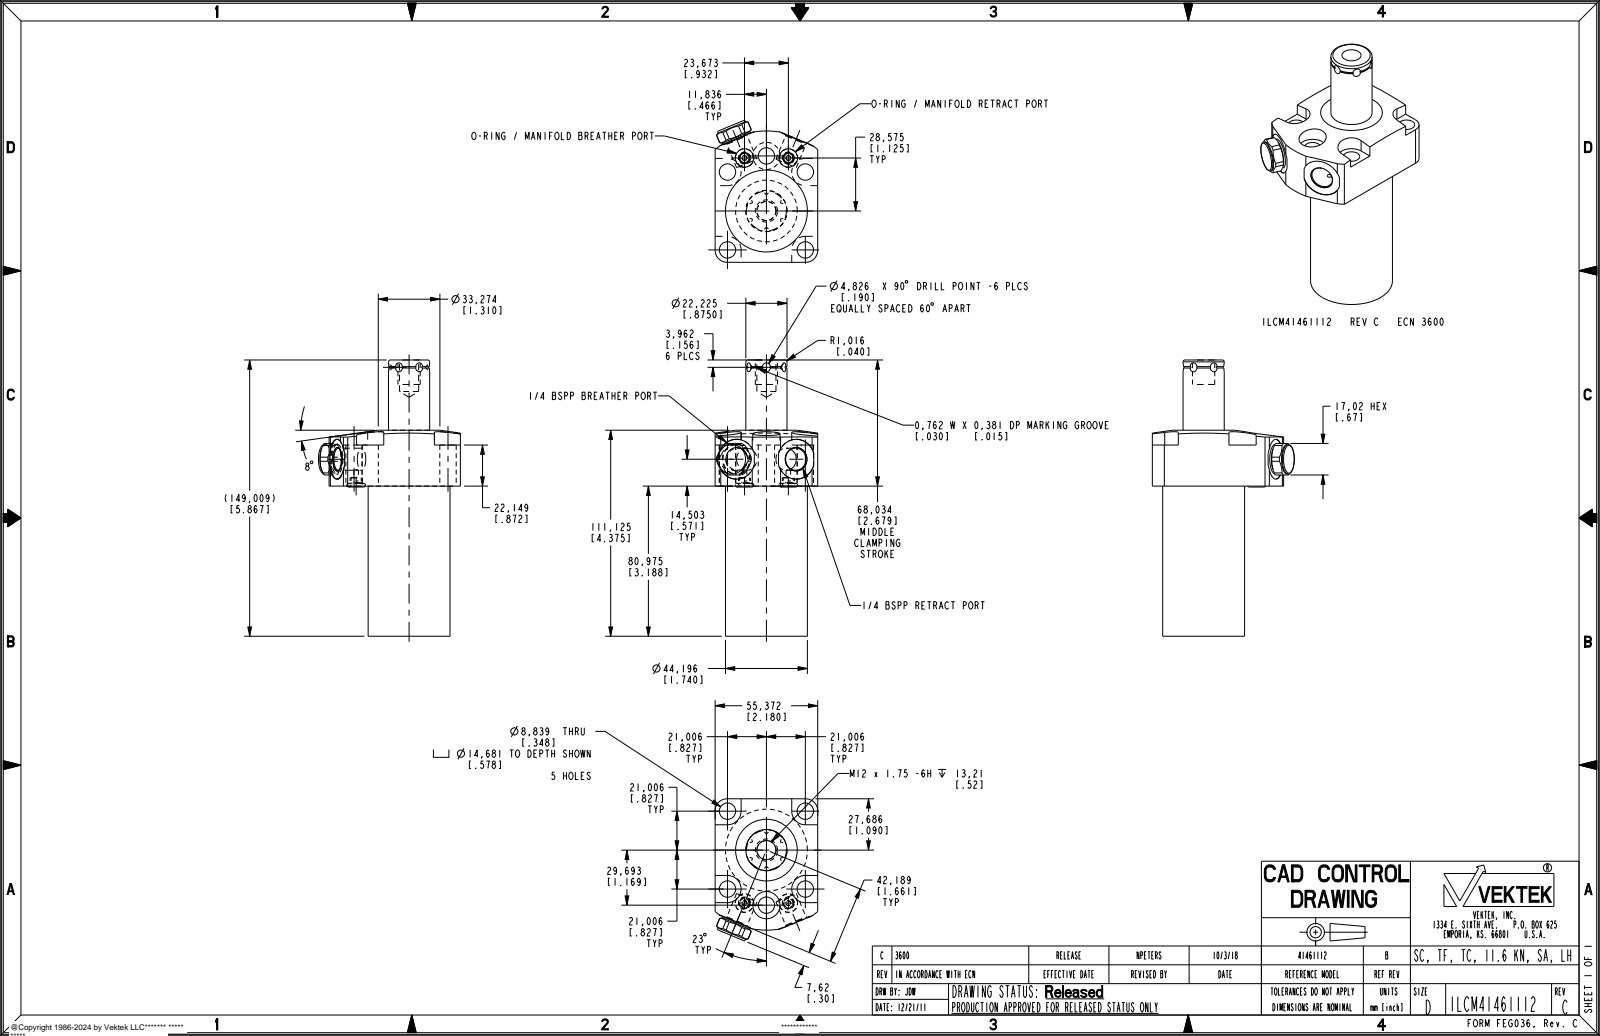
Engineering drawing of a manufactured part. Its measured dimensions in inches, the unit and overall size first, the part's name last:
Units: inches
Overall size (bounding box): 5.867 × 3.017 × 2.18
Round holes (diameter × count): ⌀0.348 ×5, ⌀0.098 ×2, ⌀0.256 ×2, ⌀0.392 ×2, ⌀0.468 ×2, ⌀0.846 ×2, ⌀0.406 ×1, ⌀0.578 ×1
Round bosses / shafts (diameter × count): ⌀0.216 ×2, ⌀1.74 ×1, ⌀0.875 ×1, ⌀0.631 ×1, ⌀0.472 ×1
Partial cylindrical surfaces — rounded edges, fillets, slot ends (radius × count): R0.289 ×4, R0.255 ×2, R0.364 ×1, R0.422 ×1, R1.7 ×1
Main face-to-face distances: 3.188, 2.18, 4.06, 0.872, 4.375, 1.187, 0.315, 5.866, 2.678, 1.806
Hole centre spacings: 1.17, 1.654, 0.468, 0.468, 0.895, 1.218, 1.327, 1.985
Volume: 14.08 in³ · Surface area: 53.37 in²
Bodies: 3 solids, 186 faces (71 planar, 71 cylindrical, 44 other)
Part name (STEP PRODUCT): ILCM41461112
STEP written by: PRO/ENGINEER BY PARAMETRIC TECHNOLOGY CORPORATION, 2013320 (AUTOMOTIVE_DESIGN)
